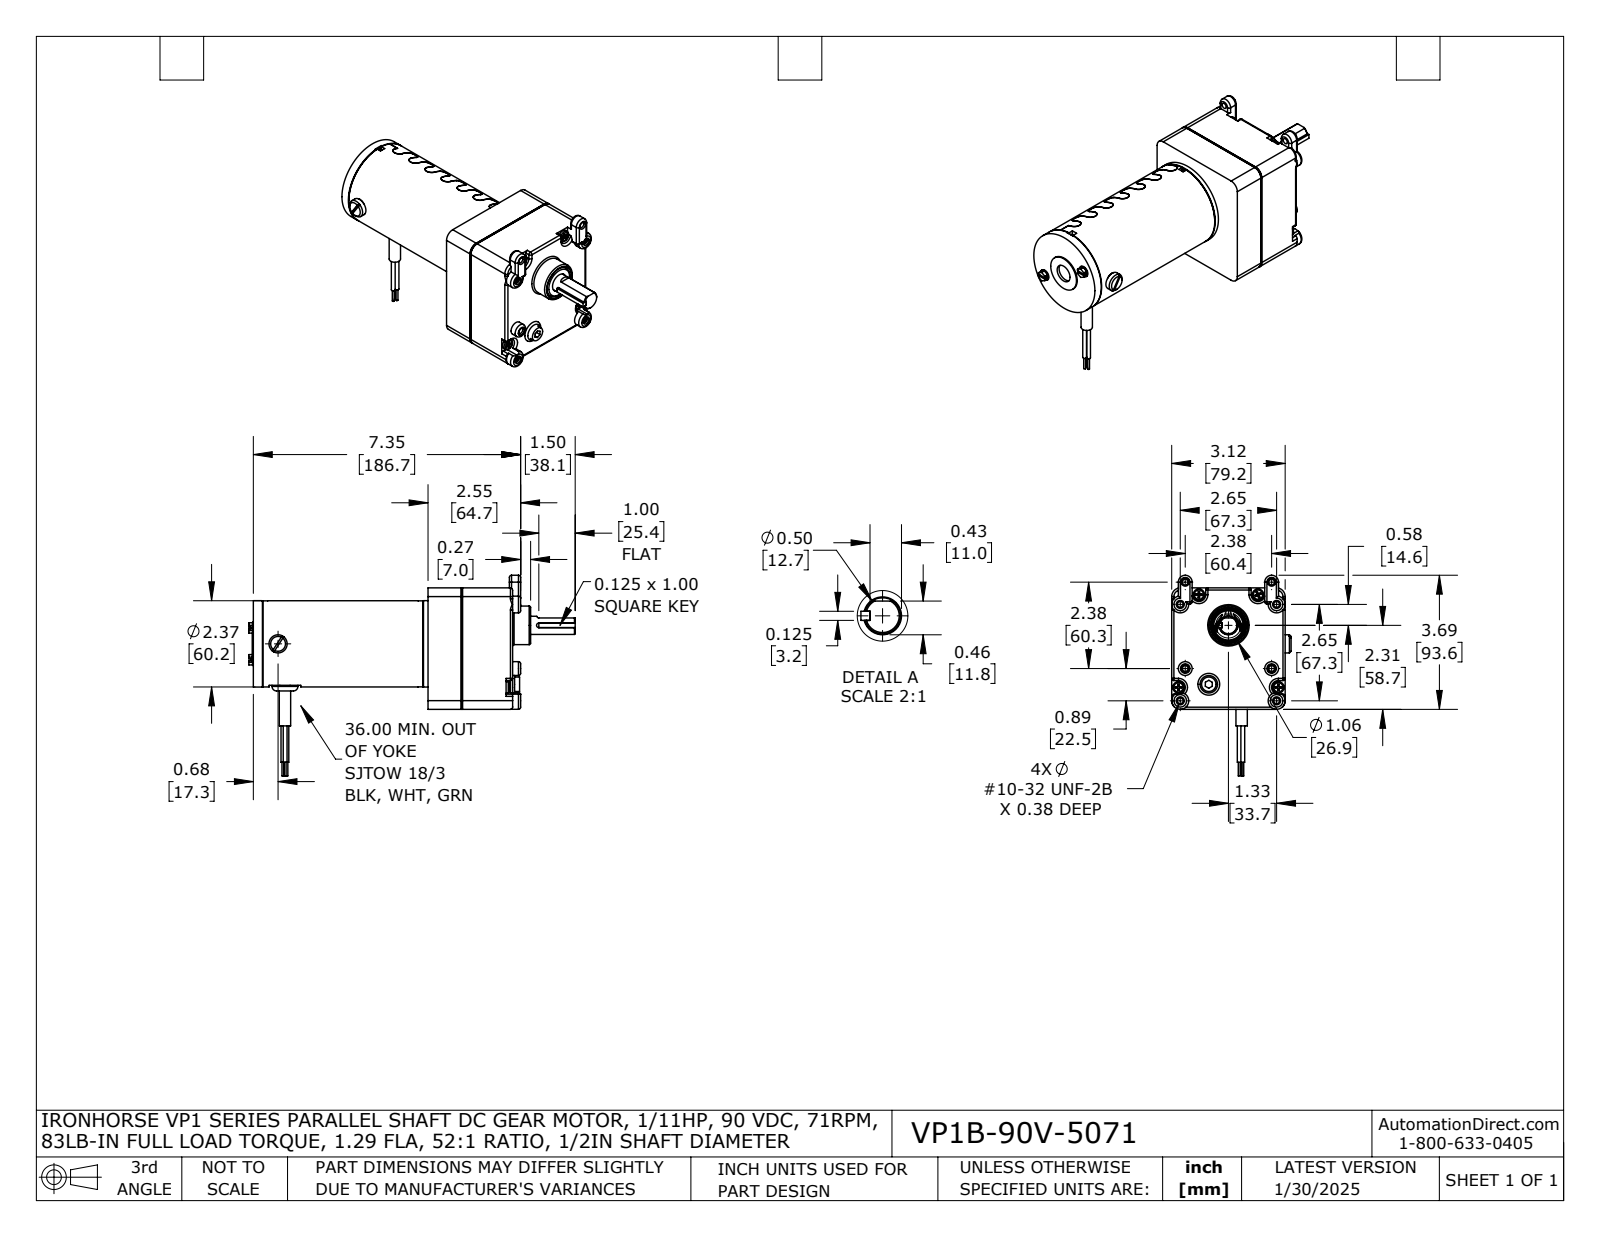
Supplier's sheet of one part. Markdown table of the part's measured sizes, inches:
| quantity | value |
| --- | --- |
| part name | VP1B-90V-5071 |
| STEP written by | SolidWorks 2021 (AUTOMOTIVE_DESIGN) |
| units | inches |
| bodies | 20 solids, 916 faces (340 planar, 422 cylindrical, 154 other) |
| overall size | 8.974 × 5.516 × 3.283 |
| volume | 12.28 in³ |
| surface area | 225.5 in² |
| round holes (diameter × count) | 0.2 × 11, 0.158 × 8, 0.18 × 4, 0.187 × 2, 0.189 × 2, 0.22 × 2, 0.213 × 1, 0.336 × 1, 0.468 × 1, 0.5 × 1, 0.521 × 1, 0.688 × 1 |
| round bosses / shafts (diameter × count) | 0.314 × 4, 0.313 × 4, 0.136 × 4, 0.105 × 3, 0.052 × 3, 0.5 × 2, 0.466 × 2, 0.44 × 2 |
| partial cylindrical surfaces (radius × count) | 0.06 × 34, 0.062 × 21, 0.156 × 14, 0.151 × 7, 0.161 × 7, 0.15 × 6, 0.12 × 4, 0.235 × 4 |
| main face-to-face distances | 0.09, 3.12, 1.38, 2.326, 0.946, 0.106, 1.274, 2.22, 3.34, 0.315 |
| hole center spacings | 1.68, 2.65, 1.074, 2.729, 3.093, 0.077, 0.297, 0.373 |
